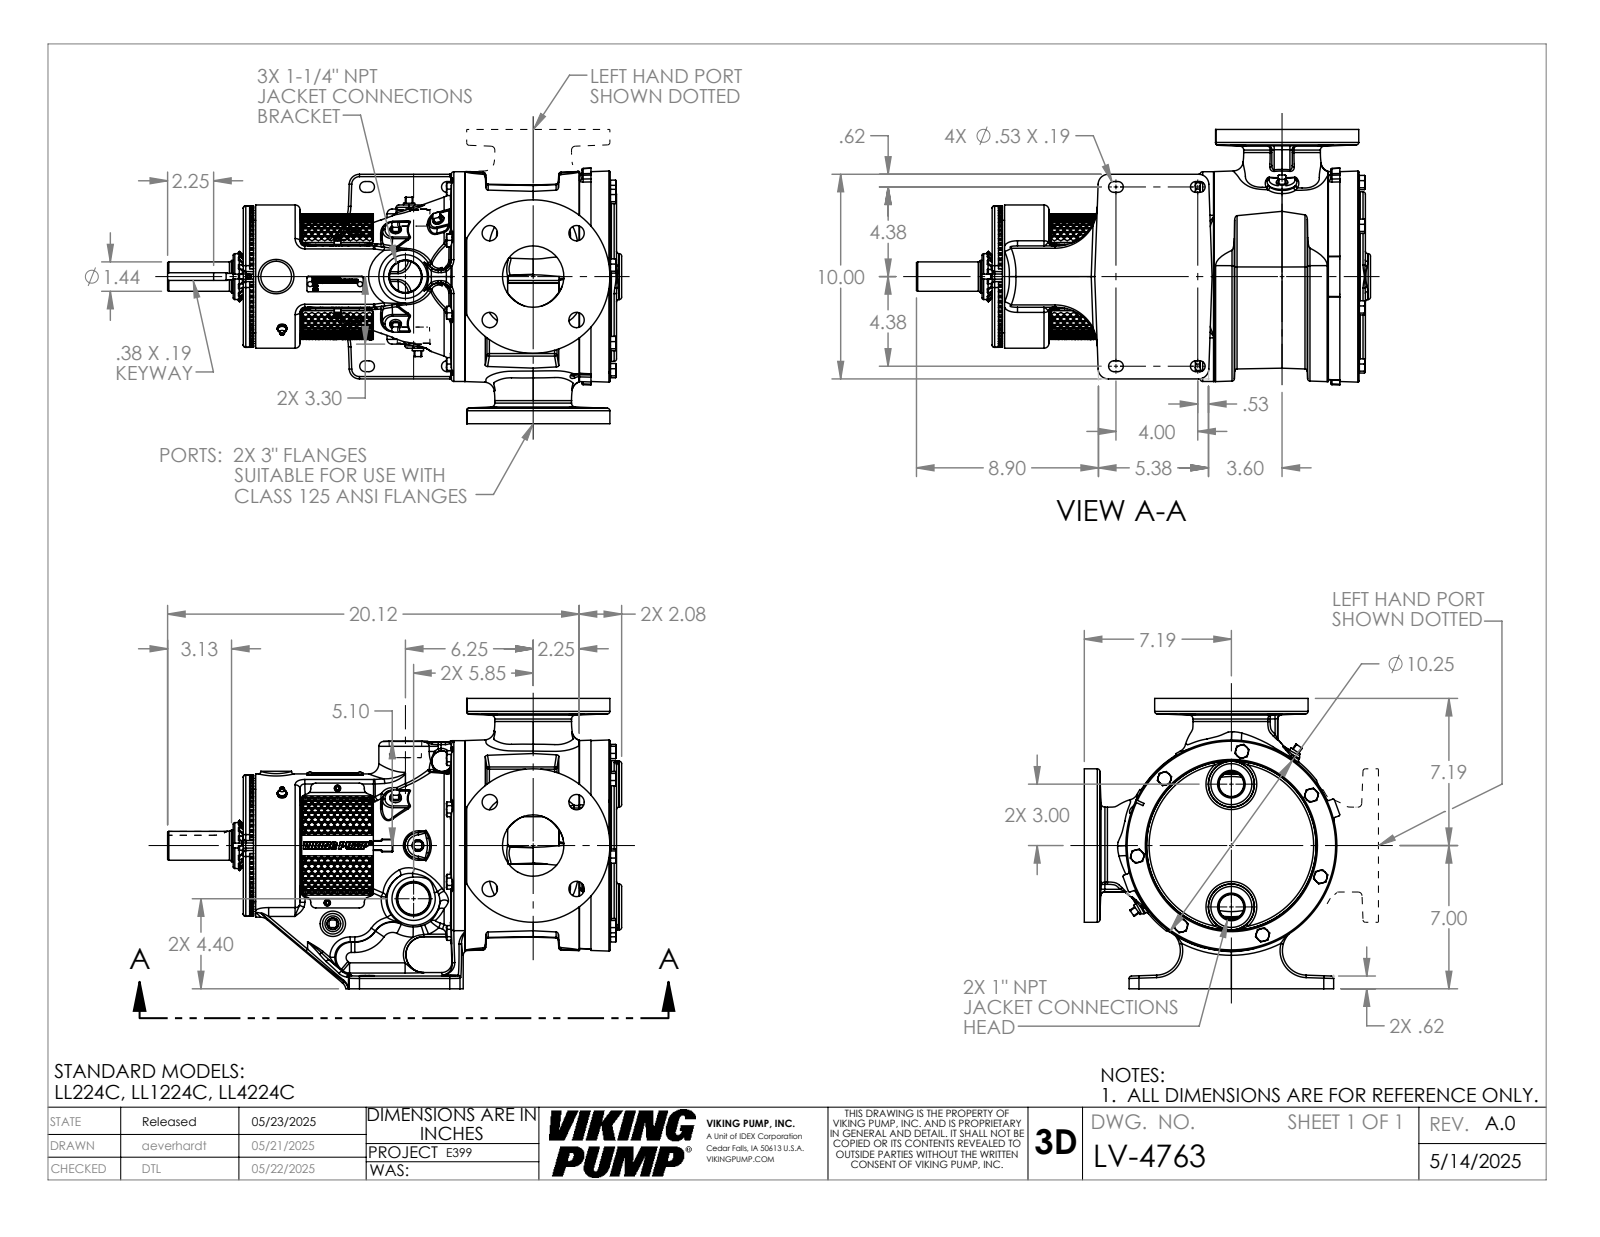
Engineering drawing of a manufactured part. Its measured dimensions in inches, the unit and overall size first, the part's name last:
Units: inches
Overall size (bounding box): 22.197 × 14.19 × 12.489
Round holes (diameter × count): ⌀0.75 ×8, ⌀1.094 ×8, ⌀0.199 ×6, ⌀0.25 ×6, ⌀0.159 ×3, ⌀0.266 ×2, ⌀0.313 ×2, ⌀1.577 ×1, ⌀1.593 ×1, ⌀1.83 ×1, ⌀2.44 ×1, ⌀5.25 ×1
Round bosses / shafts (diameter × count): ⌀0.625 ×11, ⌀0.625 ×4, ⌀0.437 ×3, ⌀0.312 ×3, ⌀7.5 ×2, ⌀3.75 ×2, ⌀10.25 ×1, ⌀7 ×1
Partial cylindrical surfaces — rounded edges, fillets, slot ends (radius × count): R0.063 ×109, R0.12 ×81, R0.069 ×74, R0.5 ×26, R0.03 ×18, R0.24 ×16, R0.06 ×13, R0.25 ×12
Main face-to-face distances: 14.19, 0.31, 0.5, 1.5, 15.187, 15.497, 2.25, 3.537, 11.65, 11.96
Hole centre spacings: 3, 4.243, 1.375, 2.18, 3.609, 4.446, 4.625, 6.404
Volume: 1 071 in³ · Surface area: 1 375 in²
Bodies: 1 solid, 4072 faces (1338 planar, 777 cylindrical, 1957 other)
Part name (STEP PRODUCT): LV-4763
STEP written by: SolidWorks 2024 (AUTOMOTIVE_DESIGN)
